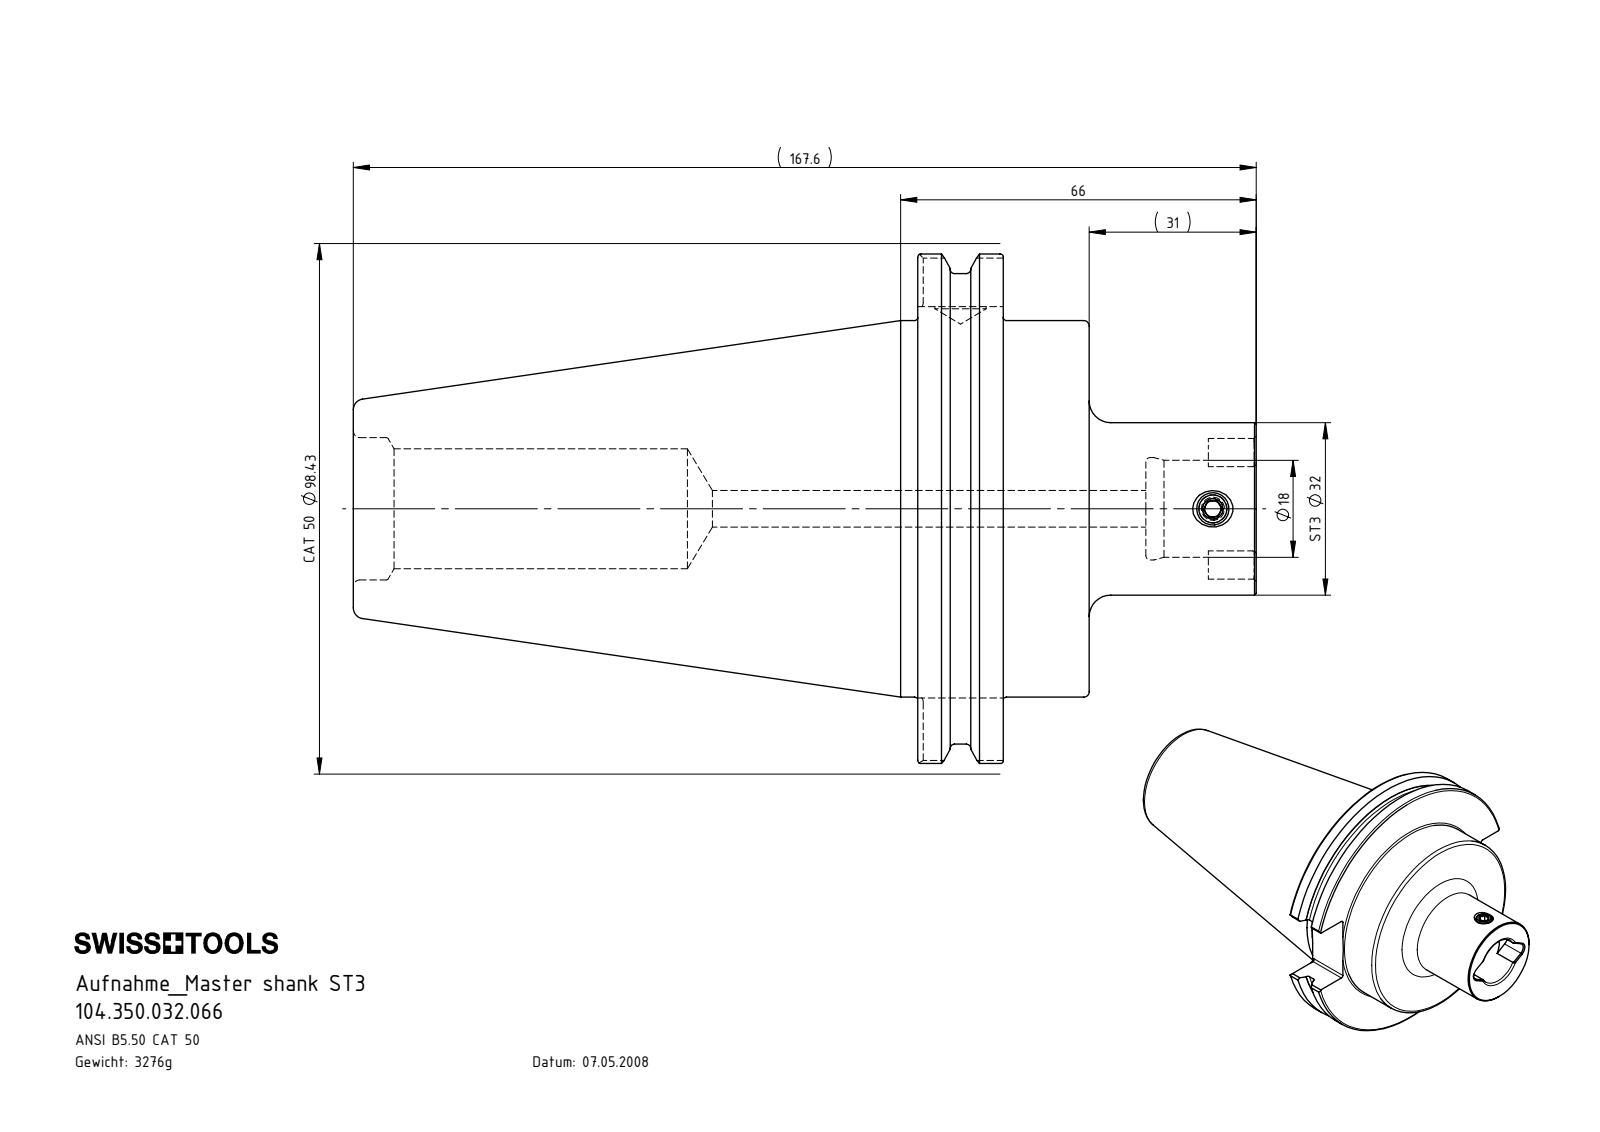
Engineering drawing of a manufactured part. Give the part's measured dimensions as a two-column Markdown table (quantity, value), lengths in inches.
| quantity | value |
| --- | --- |
| part name | CT5-ST3.K01.066_B; CT5.ST3.K01.066; ST3-ER1.001.008_A |
| STEP written by | SolidWorks 2017 (AUTOMOTIVE_DESIGN) |
| units | inches |
| bodies | 2 solids, 115 faces (50 planar, 28 cylindrical, 37 other) |
| overall size | 6.598 × 3.875 × 3.721 |
| volume | 25.47 in³ |
| surface area | 77.29 in² |
| round holes (diameter × count) | 0.118 × 1, 0.207 × 1, 0.268 × 1, 0.374 × 1, 0.709 × 1, 0.748 × 1, 0.876 × 1, 1.039 × 1 |
| round bosses / shafts (diameter × count) | 3.875 × 1, 3.583 × 1, 2.75 × 1, 1.26 × 1, 0.236 × 1 |
| partial cylindrical surfaces (radius × count) | 0.031 × 8, 0.098 × 2 |
| main face-to-face distances | 0.625, 1.253, 0.628, 2.473, 1.848, 1.22, 4.125, 4.75, 5.378, 6.598 |
